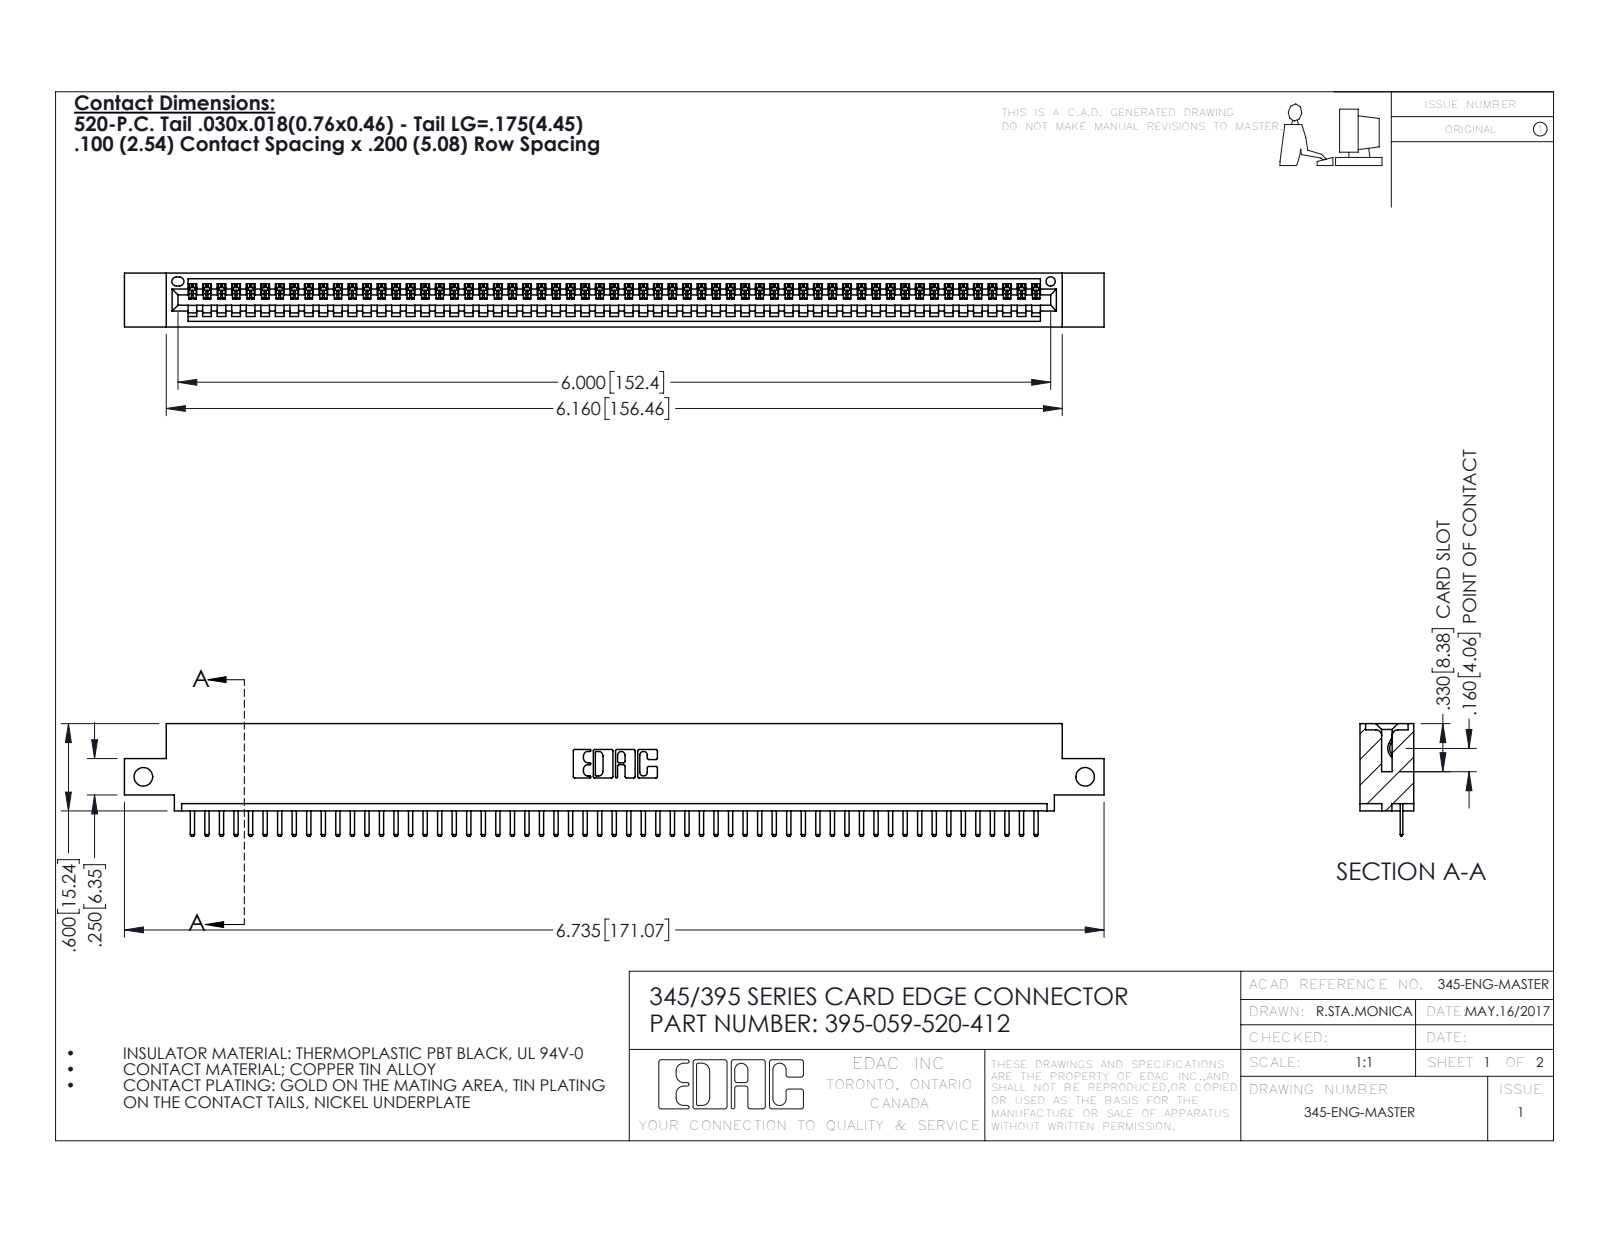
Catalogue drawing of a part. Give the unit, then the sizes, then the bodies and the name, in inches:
Units: inches
Overall size (bounding box): 6.735 × 0.775 × 0.37
Round holes (diameter × count): ⌀0.128 ×2, ⌀0.064 ×1
Partial cylindrical surfaces — rounded edges, fillets, slot ends (radius × count): R0.01 ×120, R0.006 ×118, R0.01 ×22, R0.007 ×6, R0.031 ×6, R0.026 ×3, R0.031 ×2, R0.04 ×2
Main face-to-face distances: 0.298, 0.072, 0.37, 0.2, 0.098, 0.272, 0.025, 0.225, 0.072, 0.149
Hole centre spacings: 6.475
Volume: 0.98 in³ · Surface area: 32.48 in²
Bodies: 60 solids, 3788 faces (2562 planar, 1226 cylindrical, 0 other)
Part name (STEP PRODUCT): 345 Part_0.110 Offset - Side Mount; 345-292-001_345-293-120; 395-059-520-412
STEP written by: SolidWorks 2016 (CONFIG_CONTROL_DESIGN)
